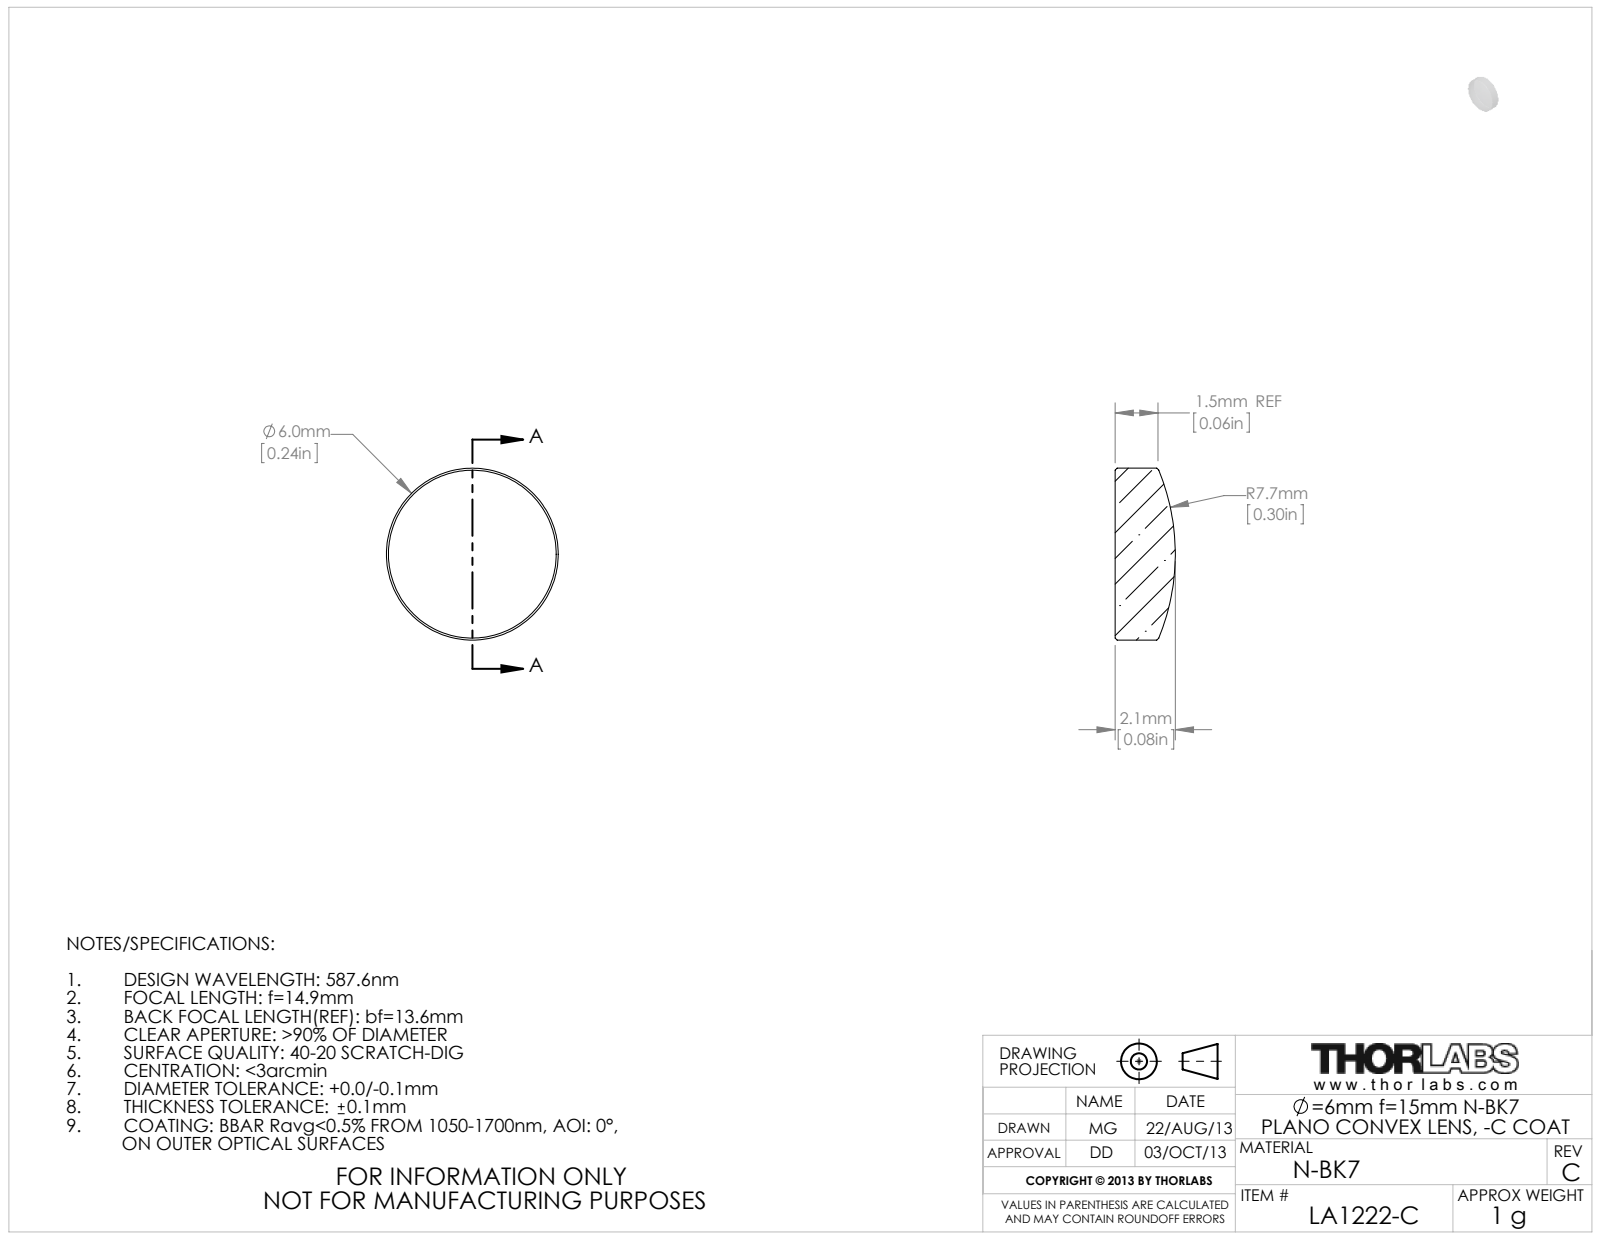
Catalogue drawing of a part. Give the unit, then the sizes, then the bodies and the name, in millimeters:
Units: millimetres
Overall size (bounding box): 6 × 6 × 2.1
Round bosses / shafts (diameter × count): ⌀6 ×1
Volume: 51 mm³ · Surface area: 86 mm²
Bodies: 1 solid, 5 faces (1 planar, 2 cylindrical, 2 other)
Part name (STEP PRODUCT): 4564-E0W
STEP written by: SolidWorks 2009 (AUTOMOTIVE_DESIGN)
